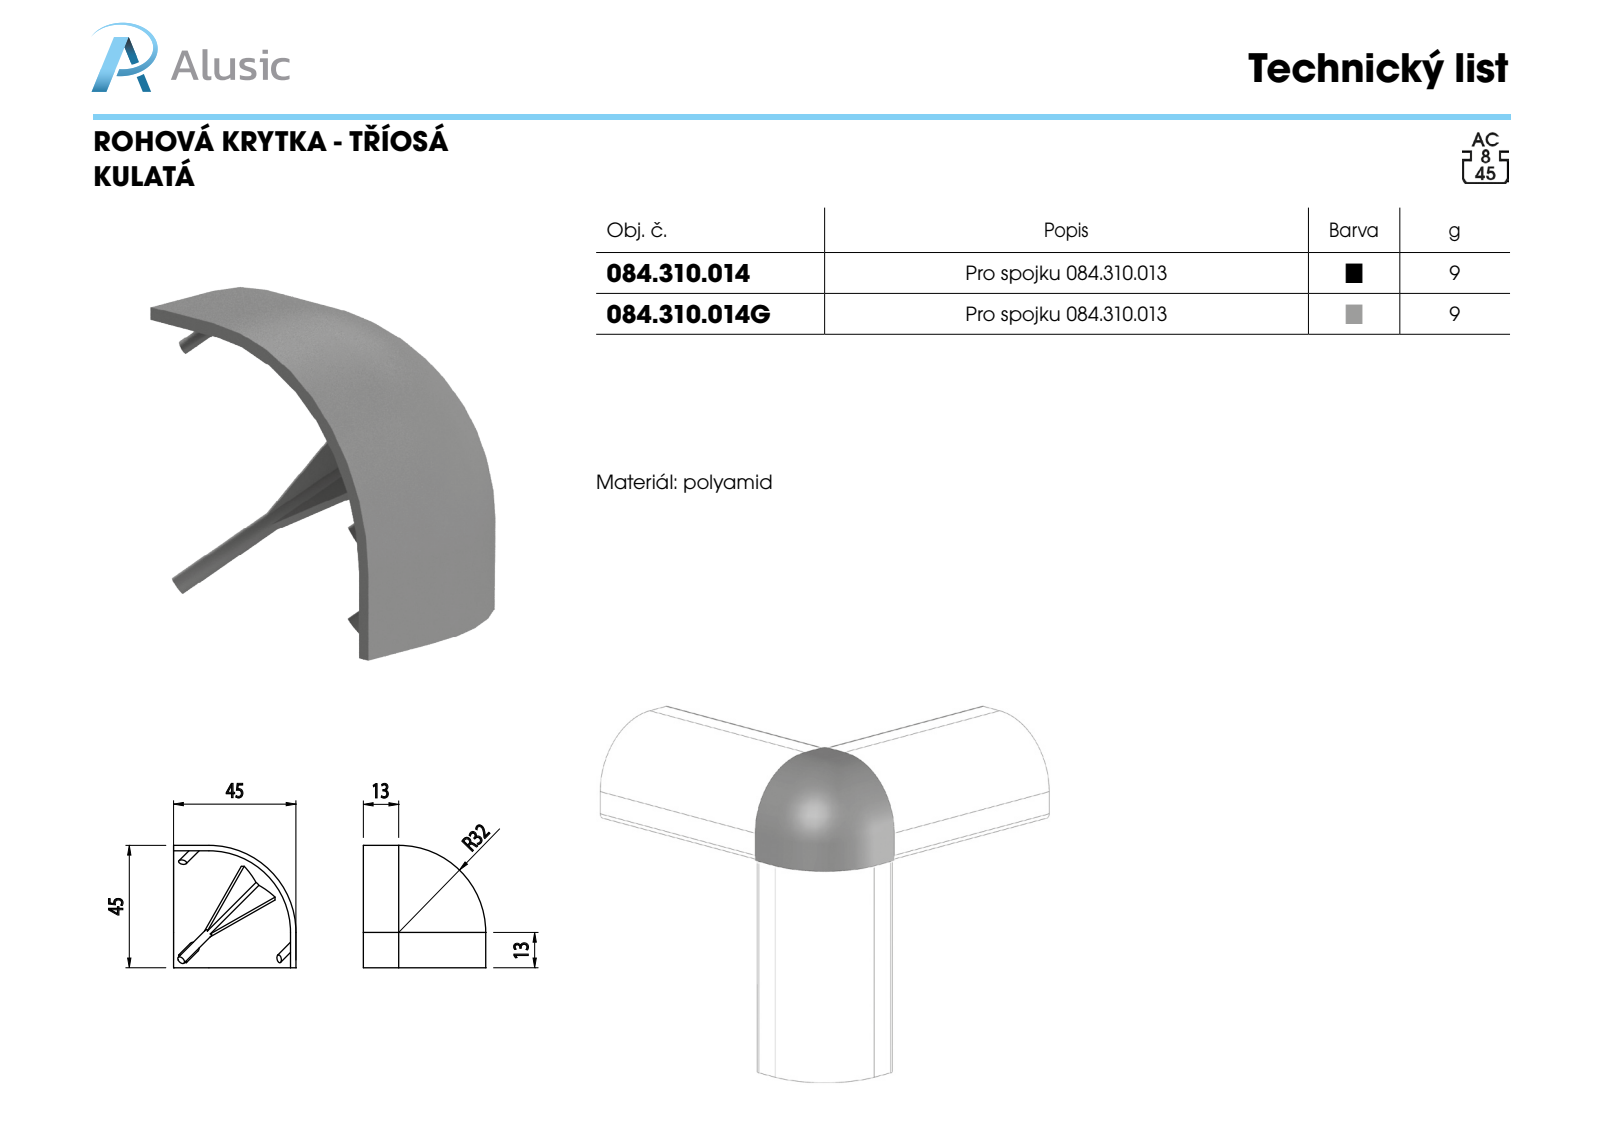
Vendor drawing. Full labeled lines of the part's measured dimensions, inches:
Part name (STEP PRODUCT): 084.310.014
STEP written by: SolidWorks 2011 (CONFIG_CONTROL_DESIGN)
Units: inches
Bodies: 1 solid, 56 faces (46 planar, 8 cylindrical, 2 other)
Overall size (bounding box): 1.772 × 1.772 × 1.772
Volume: 0.539 in³ · Surface area: 14.92 in²
Round bosses / shafts (diameter × count): ⌀0.11 ×1
Partial cylindrical surfaces — rounded edges, fillets, slot ends (radius × count): R1.181 ×3, R1.26 ×3
Main face-to-face distances: 0.079, 1.693, 1.772, 0.059, 0.049, 0.108, 0.157, 0.866
